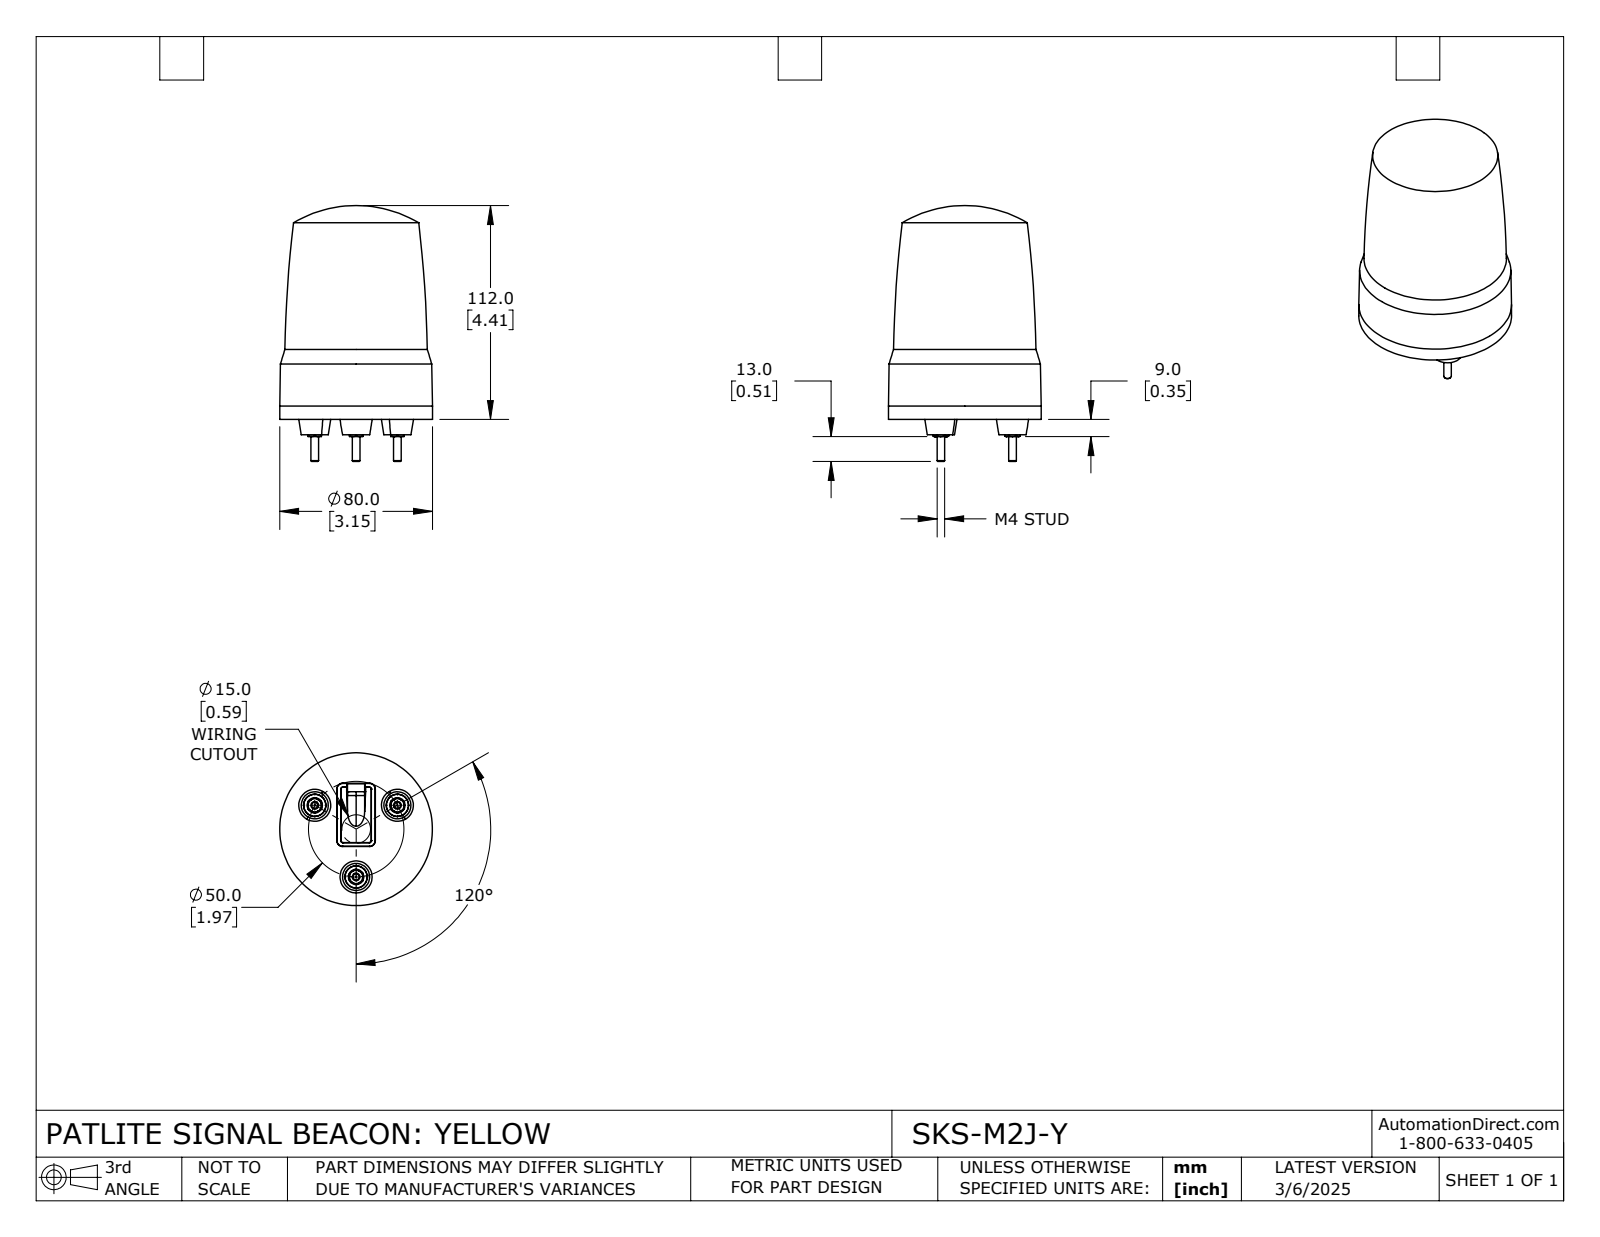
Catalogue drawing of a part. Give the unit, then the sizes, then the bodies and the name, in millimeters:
Units: millimetres
Overall size (bounding box): 134 × 80 × 80
Round bosses / shafts (diameter × count): ⌀8 ×3, ⌀4 ×3, ⌀80 ×1
Main face-to-face distances: 0.85, 2.45, 1.6, 5.3, 6.15, 7.75, 2.7, 8, 8.85, 10.45
Volume: 463 225 mm³ · Surface area: 35 408 mm²
Bodies: 1 solid, 138 faces (47 planar, 14 cylindrical, 77 other)
Part name (STEP PRODUCT): SKS-M2J-Y
STEP written by: SolidWorks 2024 (CONFIG_CONTROL_DESIGN)
